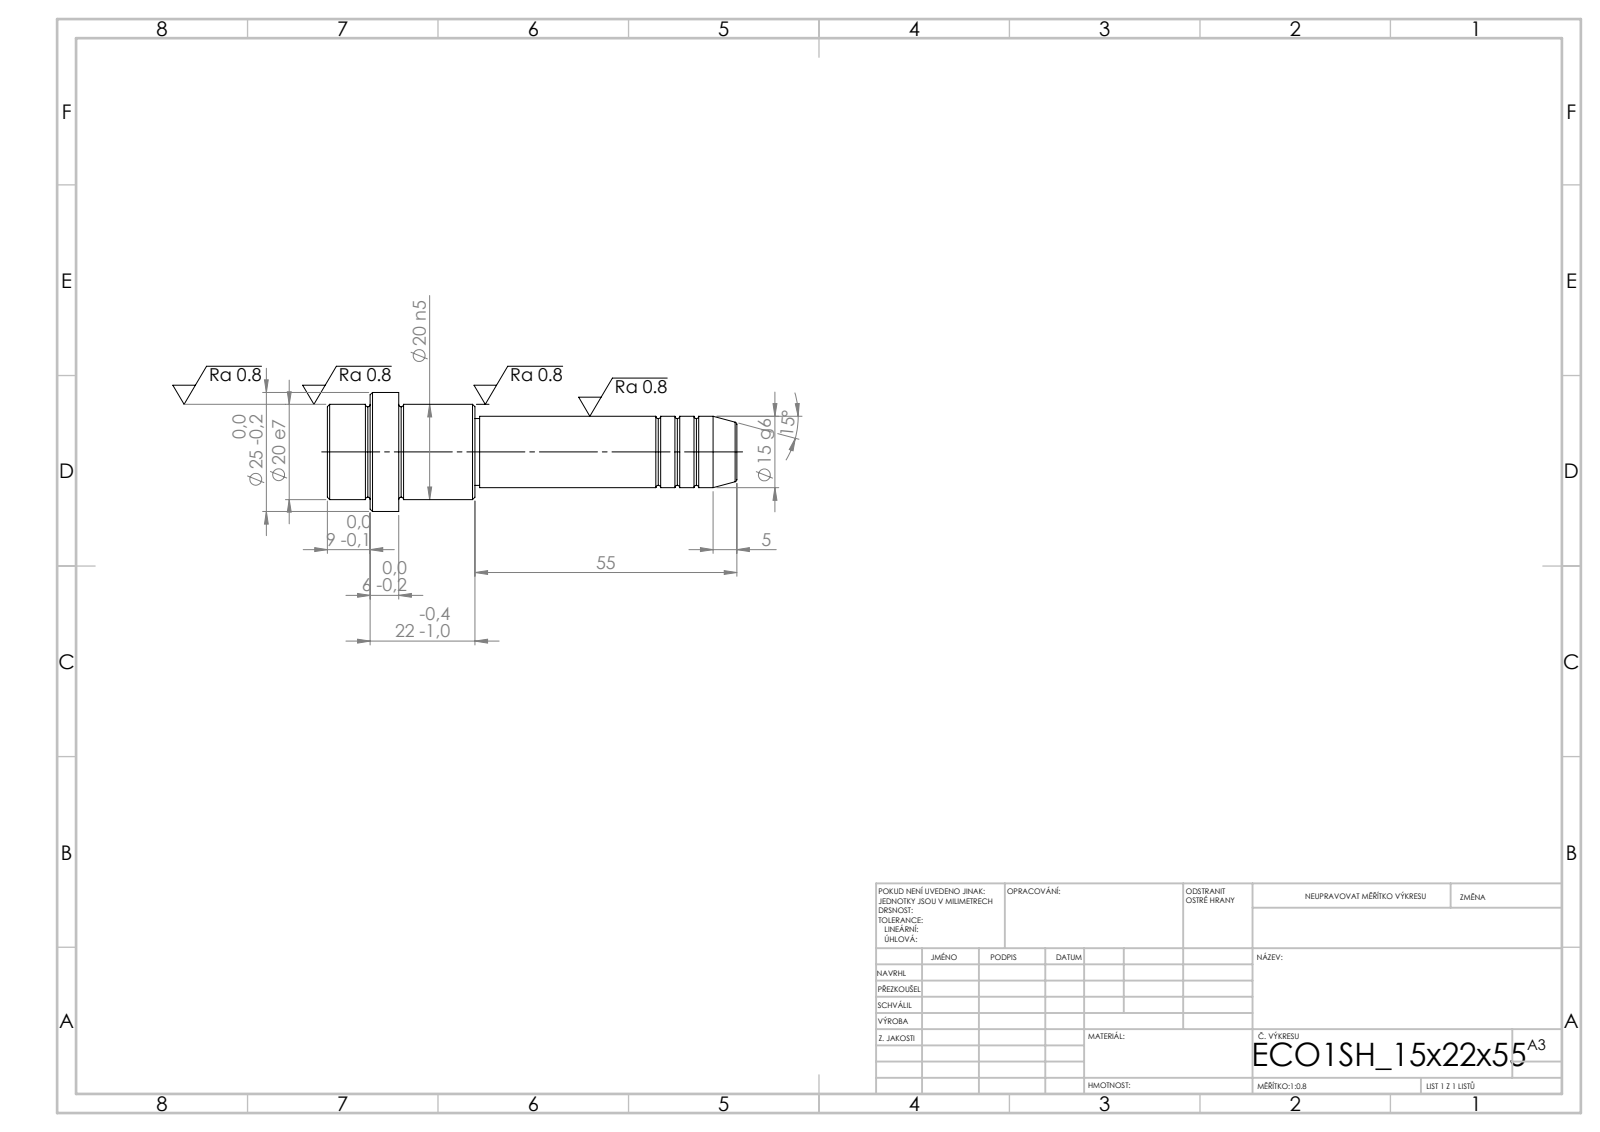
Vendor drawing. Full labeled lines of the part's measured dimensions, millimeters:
STEP written by: SolidWorks 2019 (CONFIG_CONTROL_DESIGN)
Units: millimetres
Bodies: 1 solid, 52 faces (6 planar, 16 cylindrical, 30 other)
Overall size (bounding box): 86 × 25 × 25
Volume: 20 219 mm³ · Surface area: 5 659 mm²
Round bosses / shafts (diameter × count): ⌀25 ×1, ⌀20 ×1, ⌀15 ×1, ⌀14 ×1
Main face-to-face distances: 15, 6, 9, 16, 22, 31, 55, 71, 77, 86
